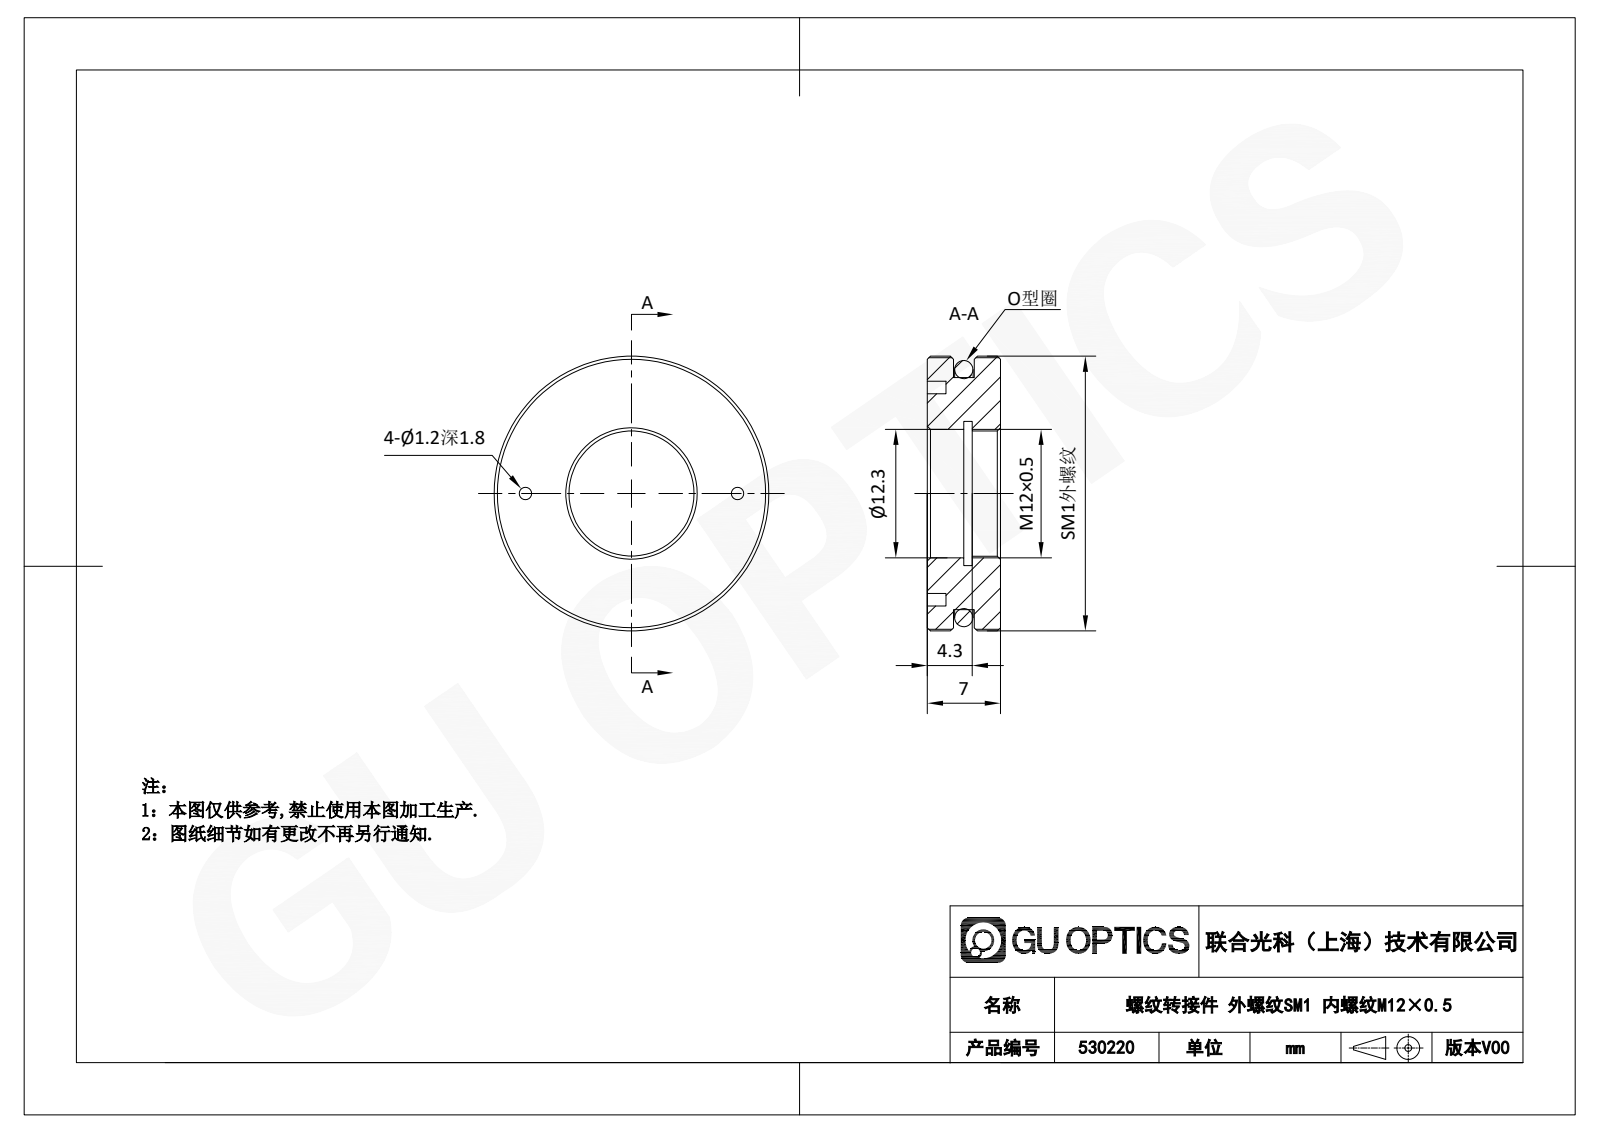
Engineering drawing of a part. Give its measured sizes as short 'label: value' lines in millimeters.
name: 530220; O型圈
written by: SolidWorks 2020 (CONFIG_CONTROL_DESIGN)
unit: mm
bodies: 2 solids, 27 faces (10 planar, 10 cylindrical, 7 other)
size: 26.29 × 26.29 × 7
volume: 2 804 mm³; area: 2 431 mm²
holes: 4× ⌀1.2, 1× ⌀12, 1× ⌀12.3, 1× ⌀13.8
bosses: 1× ⌀26.29, 1× ⌀22.2
face distances: 7, 2.5, 4.5, 2, 3.5, 1, 1.8, 2.7, 4.3, 0.8
hole spacings: 10.15, 14.35, 20.3
